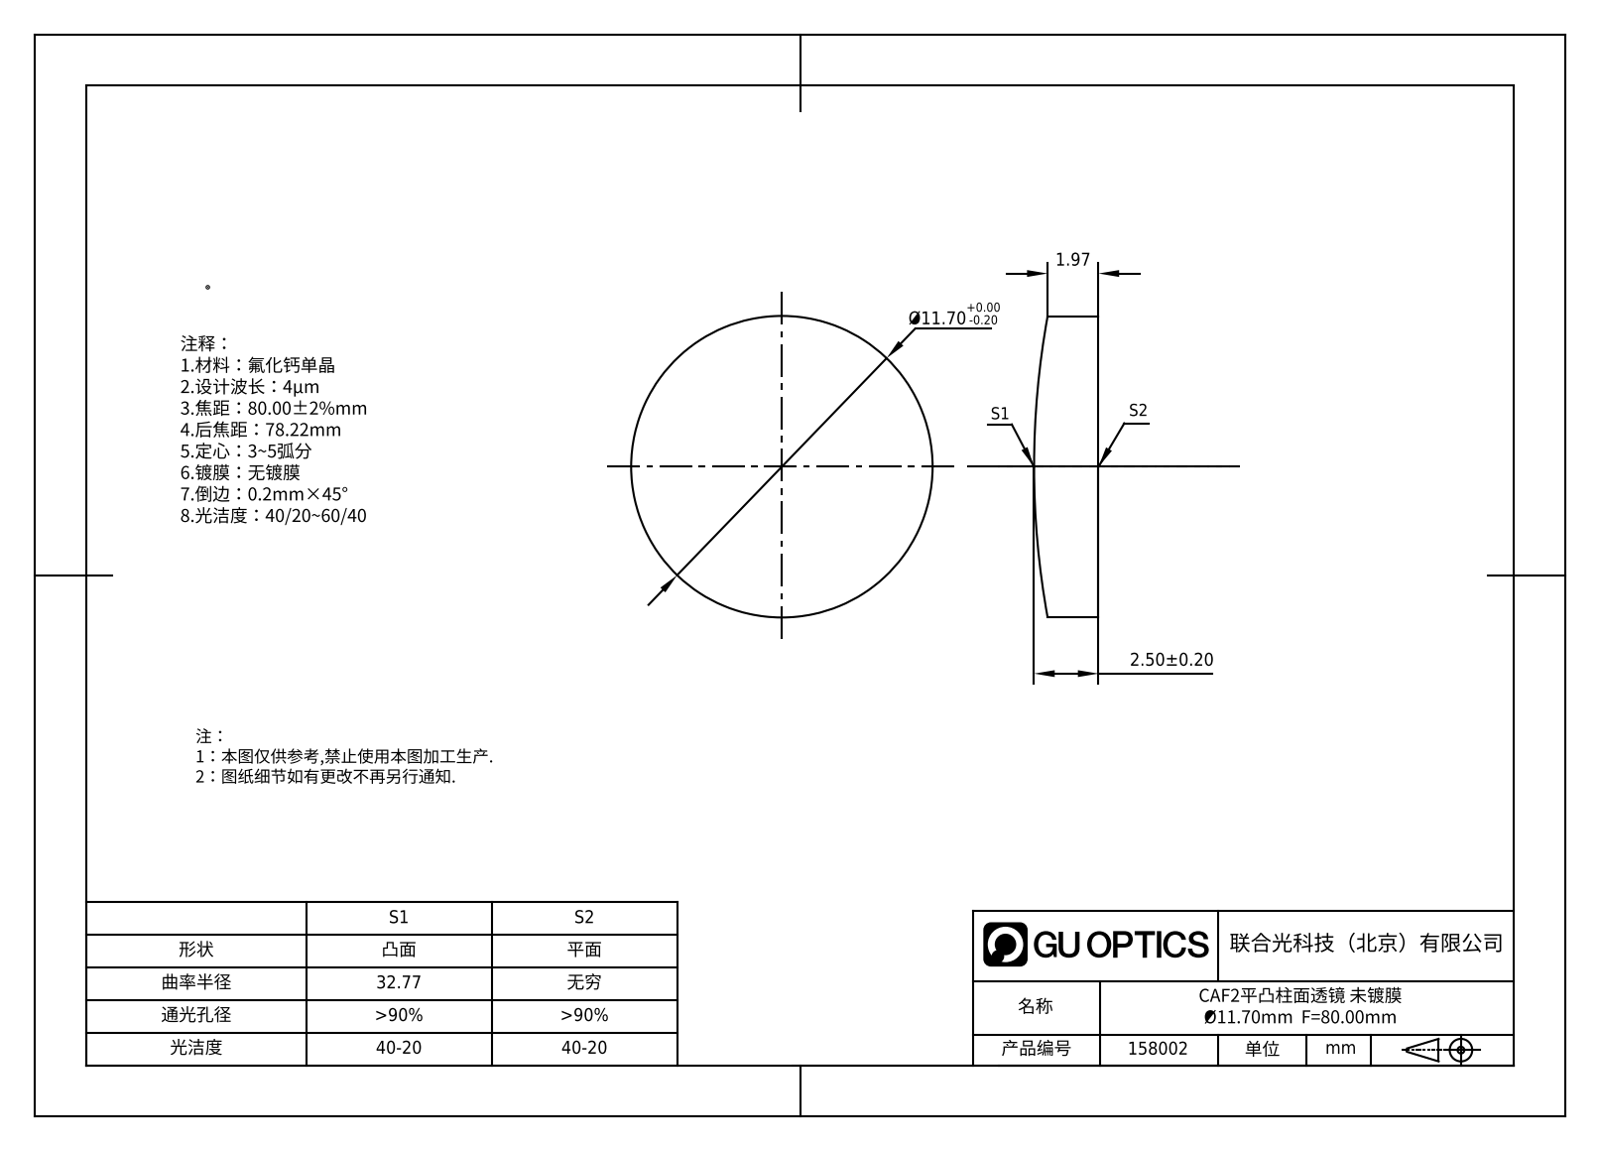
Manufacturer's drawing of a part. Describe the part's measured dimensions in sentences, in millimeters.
The part is named "GL55-012-080". Its 3-D file was written by "SolidWorks 2022 (AUTOMOTIVE_DESIGN)". It is 1 solid with 9 faces: 1 planar, 4 cylindrical and 4 other. Overall it measures 11.7 by 11.7 by 2.5 millimeters. Its volume is 253 cubic millimeters and its surface area 290 square millimeters. Round bosses or shafts: 1 of diameter 11.7. Partial cylindrical surfaces (rounded edges, fillets, slot ends): 1 of radius 32.77.
